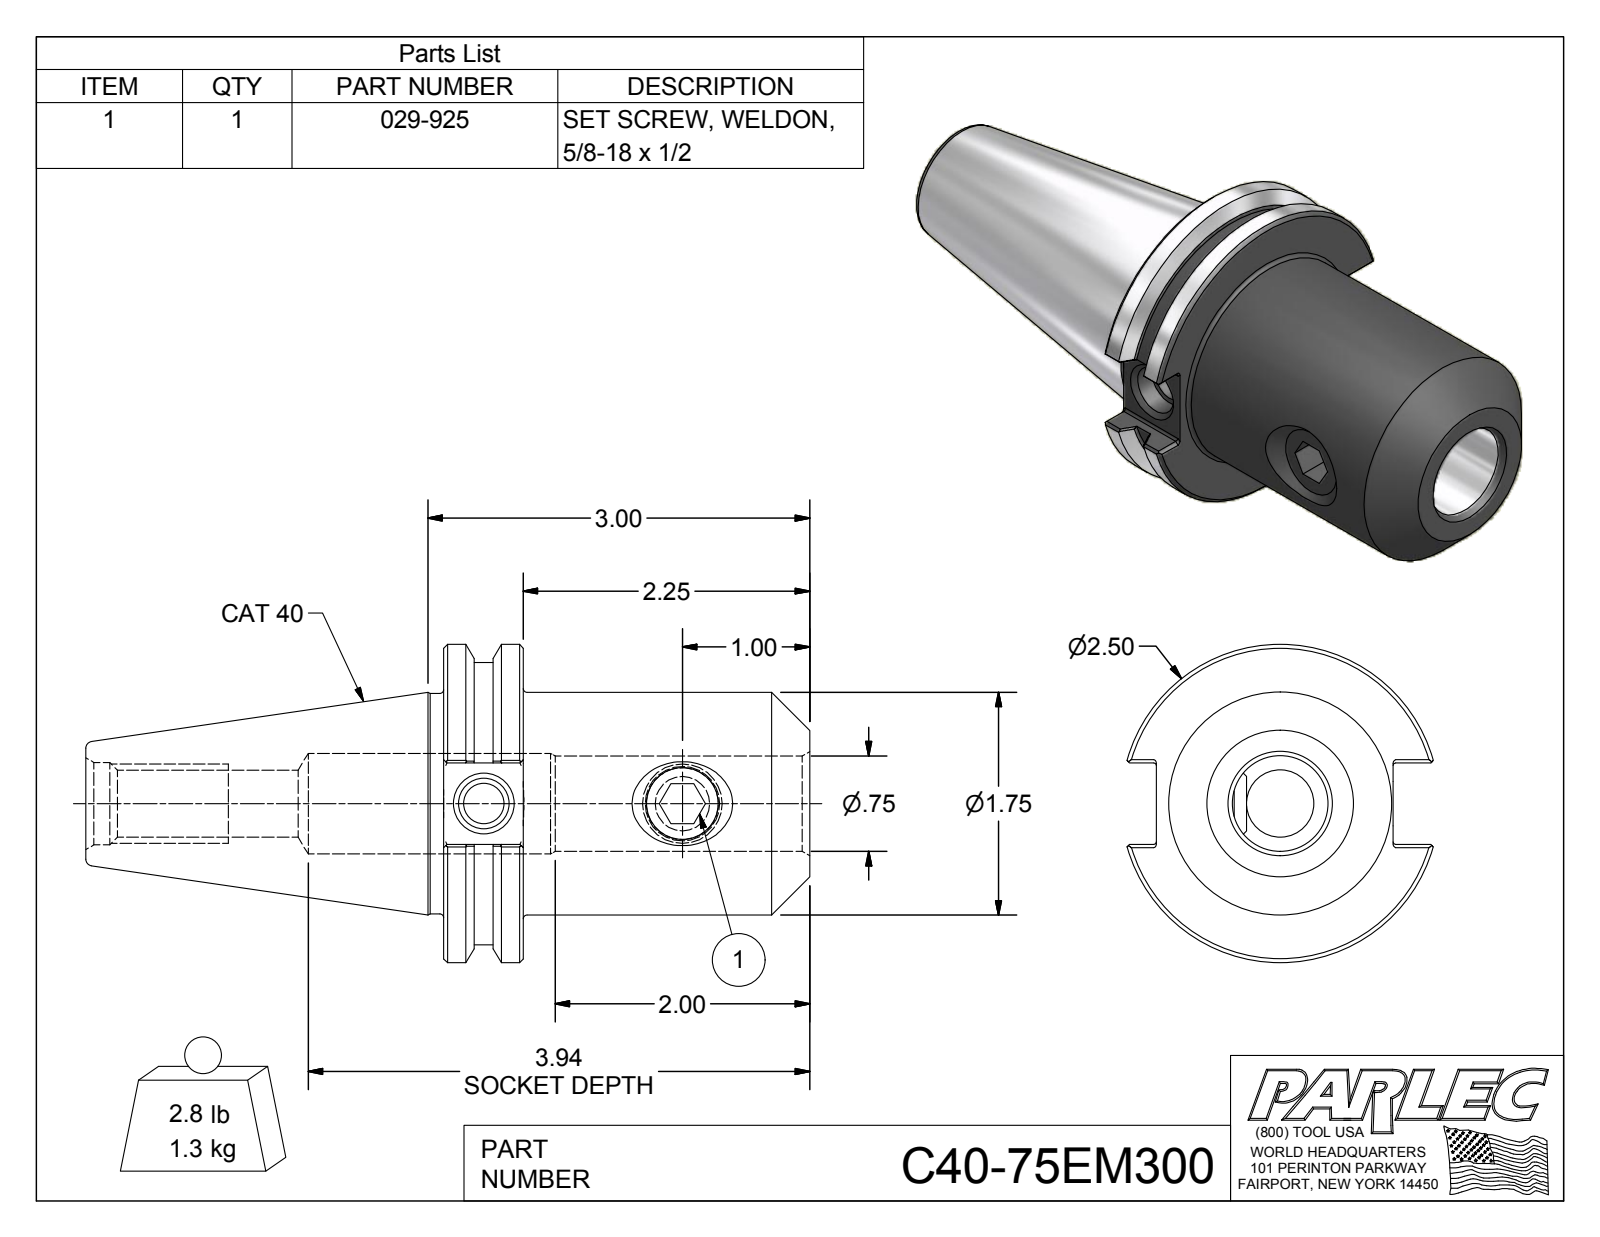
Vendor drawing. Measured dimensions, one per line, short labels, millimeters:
name: C40-75EM300; C40-75EM300-1; 029-925
written by: Autodesk Inventor 2012 (AUTOMOTIVE_DESIGN)
unit: mm
bodies: 2 solids, 100 faces (40 planar, 28 cylindrical, 32 other)
size: 144.4 × 63.5 × 61.1
volume: 160 800 mm³; area: 33 130 mm²
holes: 1× ⌀8, 1× ⌀10.1, 1× ⌀13.4, 1× ⌀14.4, 1× ⌀16.5, 1× ⌀19.1, 1× ⌀20.1
bosses: 1× ⌀63.5, 1× ⌀56.4, 1× ⌀44.5, 1× ⌀43.9, 1× ⌀15.9
rounds: 12× R0.5
face distances: 15.9, 73, 57.2, 16.3, 8, 47.2, 71.4, 87.3, 144.4, 41.9
hole spacings: 39.6
